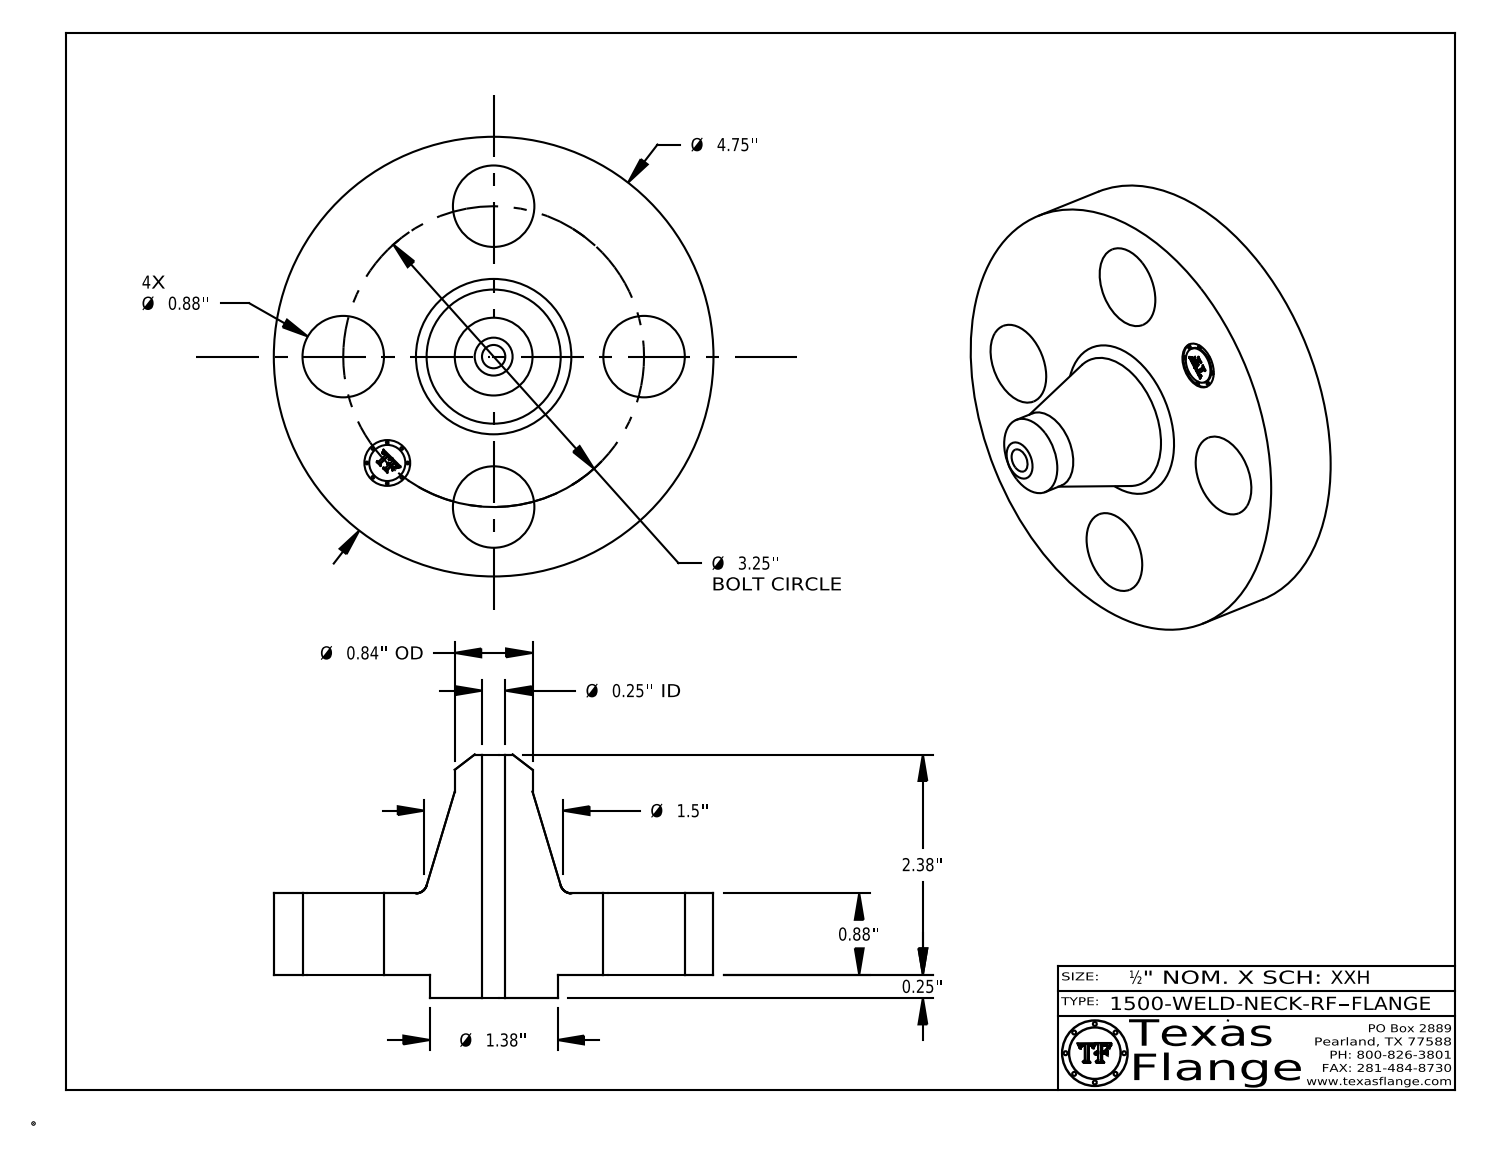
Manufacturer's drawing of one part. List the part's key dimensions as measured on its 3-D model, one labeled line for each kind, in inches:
Part name (STEP PRODUCT): 1500-WELD-NECK-RF
STEP written by: CATIA V5 STEP AP214 (AUTOMOTIVE_DESIGN)
Units: inches
Bodies: 1 solid, 411 faces (369 planar, 36 cylindrical, 6 other)
Overall size (bounding box): 4.75 × 4.75 × 2.63
Volume: 15.1 in³ · Surface area: 60.22 in²
Round holes (diameter × count): ⌀0.88 ×4, ⌀0.252 ×1, ⌀0.495 ×1
Round bosses / shafts (diameter × count): ⌀0.03 ×8, ⌀4.75 ×1, ⌀1.38 ×1, ⌀0.84 ×1, ⌀0.39 ×1
Main face-to-face distances: 0.88, 0.25, 1.13, 2.63, 2.38, 1.5, 1.115, 0.865, 0.015, 1.515
Hole centre spacings: 1.625, 2.298, 1.244, 3.003, 3.25
